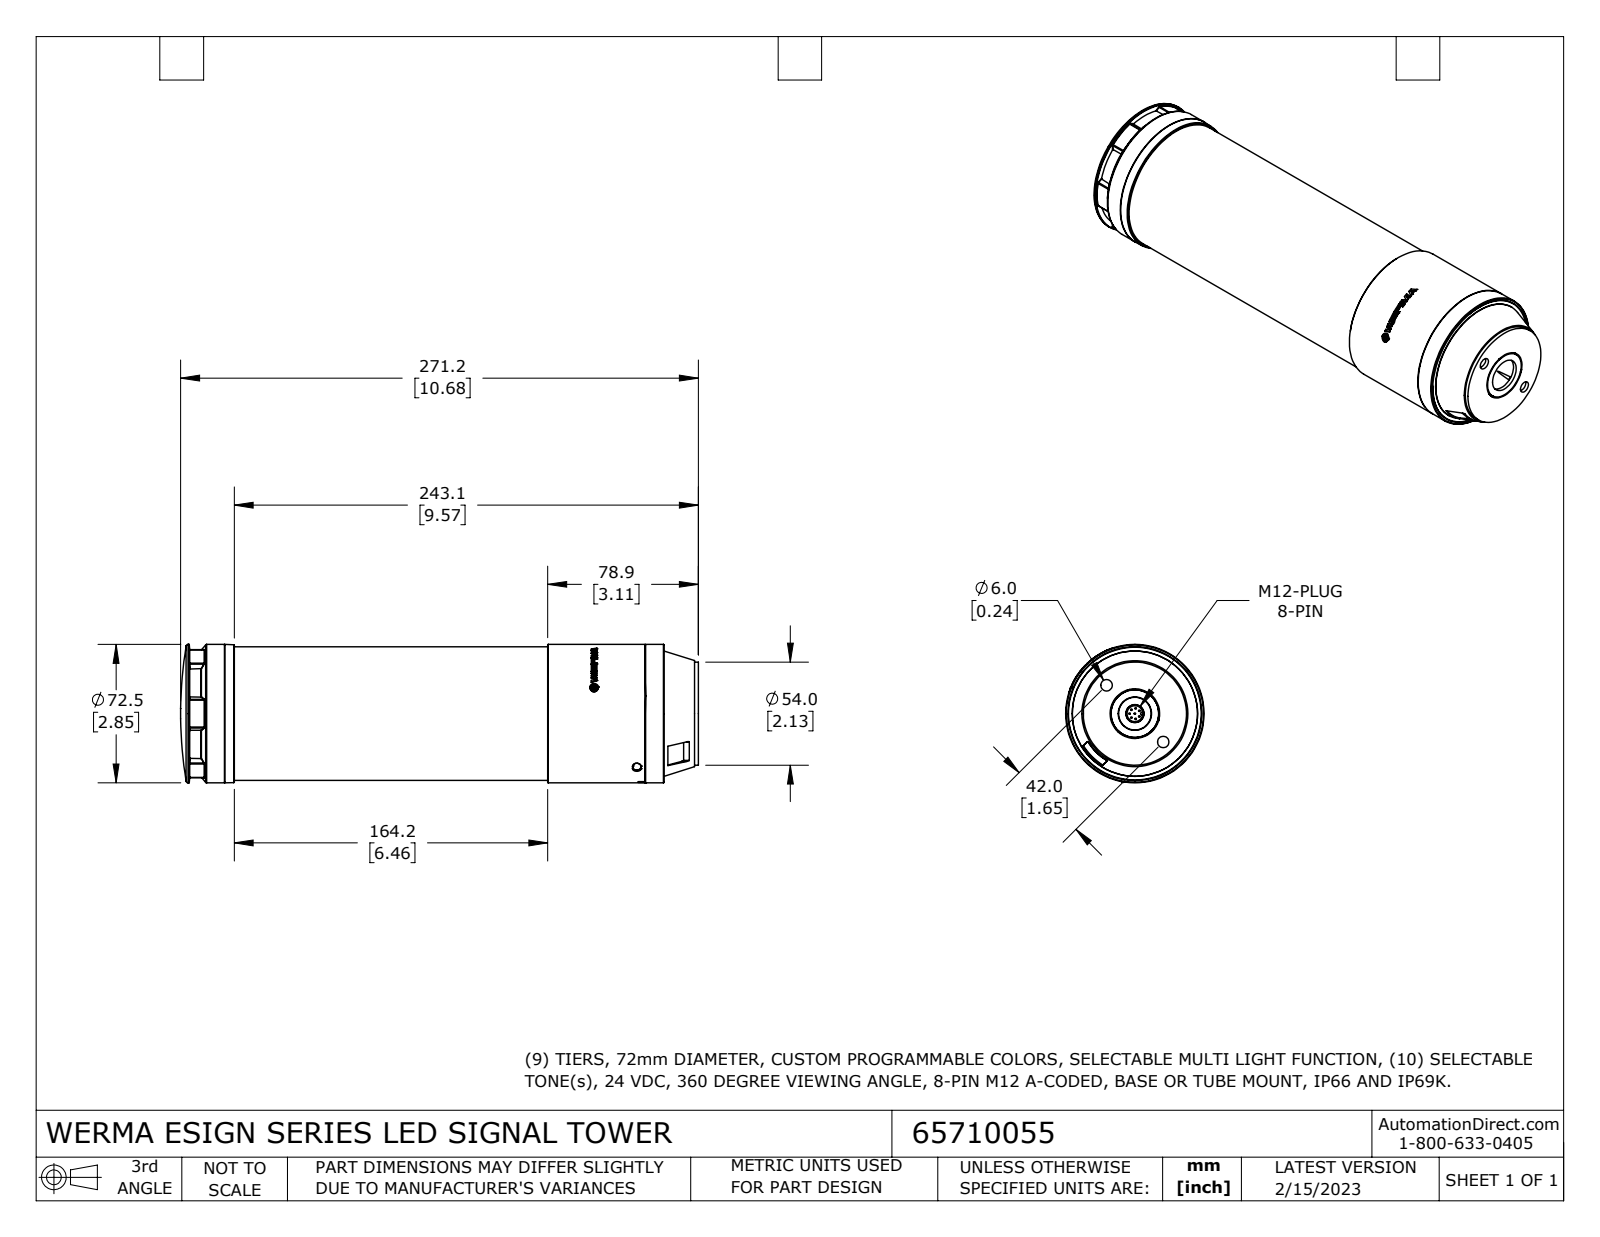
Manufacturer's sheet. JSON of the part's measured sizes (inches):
{"part_name": "65710055", "step_written_by": "SolidWorks 2021 (CONFIG_CONTROL_DESIGN)", "units": "inches", "bodies": {"solids": 1, "faces": 414, "planar": 137, "cylindrical": 127, "other": 150}, "overall_size": [10.677, 2.854, 2.854], "volume_in3": 61.12, "surface_area_in2": 122.1, "round_holes": [[0.236, 2], [0.327, 1], [0.374, 1], [0.689, 1], [1.024, 1]], "round_bosses_or_shafts": [[0.031, 8], [2.854, 1], [2.756, 1], [2.126, 1], [0.98, 1], [0.173, 1]], "partial_cylinders_radius": [[0.01, 12], [0.028, 12], [0.079, 2], [0.08, 2], [0.099, 2], [0.009, 1], [0.011, 1], [0.016, 1]], "face_to_face_distances": [10.256, 0.079, 10.177, 0.717, 0.638, 9.539, 1.004, 0.925, 0.287, 9.252], "hole_center_spacings": [0.827, 1.654]}
